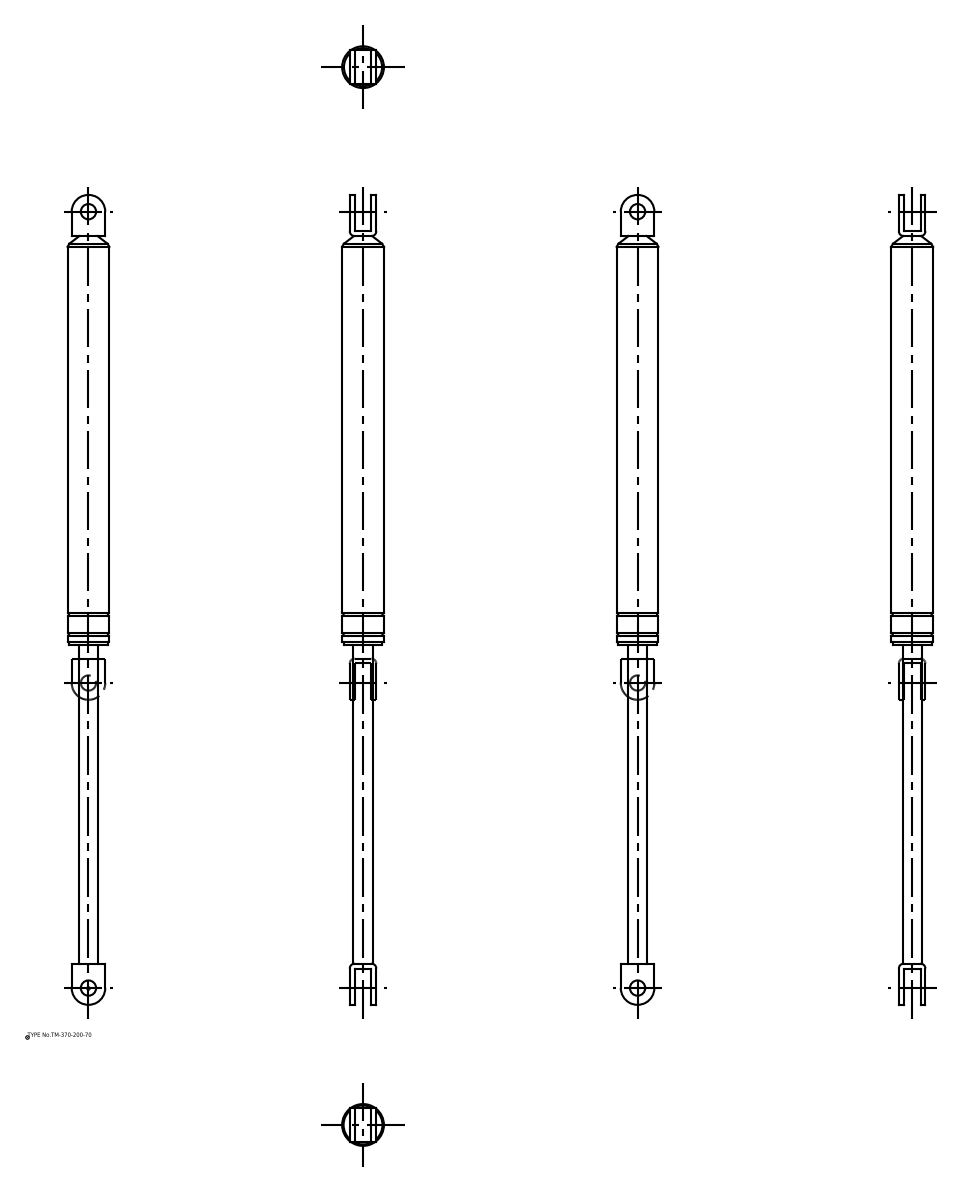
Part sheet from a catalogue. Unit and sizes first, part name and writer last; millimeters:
Units: millimetres
Overall size (bounding box): 531 × 28.2 × 28.2
Round holes (diameter × count): ⌀10 ×2
Round bosses / shafts (diameter × count): ⌀28.2 ×1, ⌀27.4 ×1, ⌀25.5 ×1, ⌀12.5 ×1
Partial cylindrical surfaces — rounded edges, fillets, slot ends (radius × count): R3.2 ×4, R11 ×2
Main face-to-face distances: 3.2, 14.2, 17.4, 11, 22, 480.2, 212.2, 483.4, 271.2, 268
Hole centre spacings: 509
Volume: 189 374 mm³ · Surface area: 38 058 mm²
Bodies: 2 solids, 64 faces (22 planar, 32 cylindrical, 10 other)
Part name (STEP PRODUCT): TM_370_200_70; TM_370_200_70_div
STEP written by: spGate 16.7.1 (AUTOMOTIVE_DESIGN)
